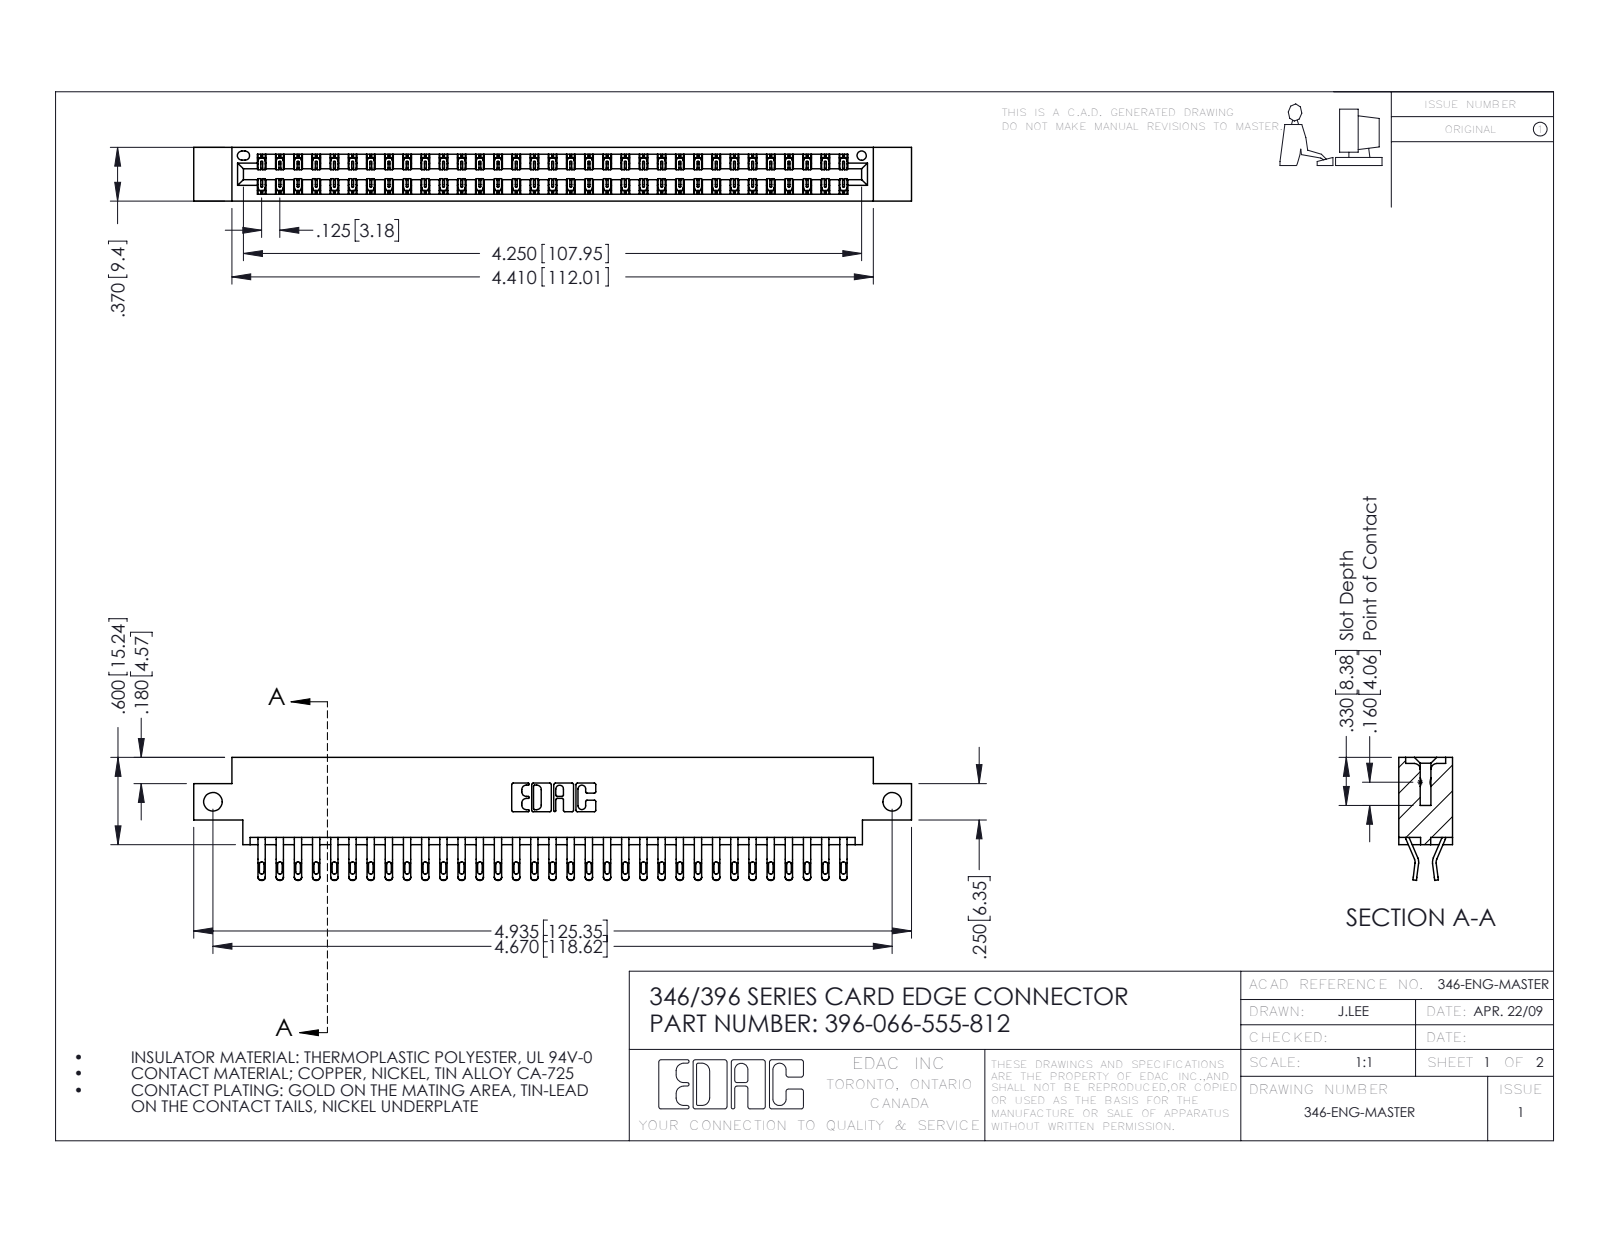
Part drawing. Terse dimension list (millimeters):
name: 396-066-555-812; 346 Part_0.170 Offset - Side Mount; 345-292-001_555 Tail
written by: SolidWorks 2016 (CONFIG_CONTROL_DESIGN)
unit: mm
bodies: 67 solids, 3954 faces (2258 planar, 1696 cylindrical, 0 other)
size: 125.3 × 21.5 × 9.4
volume: 12 100 mm³; area: 17 220 mm²
holes: 2× ⌀3.3, 1× ⌀1.6
rounds: 132× R0.4, 132× R0.5, 99× R0.2, 22× R0.3, 6× R0.2, 6× R0.8, 3× R0.7, 2× R0.3
face distances: 1.2, 8.2, 9.4, 6.4, 0.6, 1.8, 7.6, 7, 3.8, 5.6
hole spacings: 118.6
